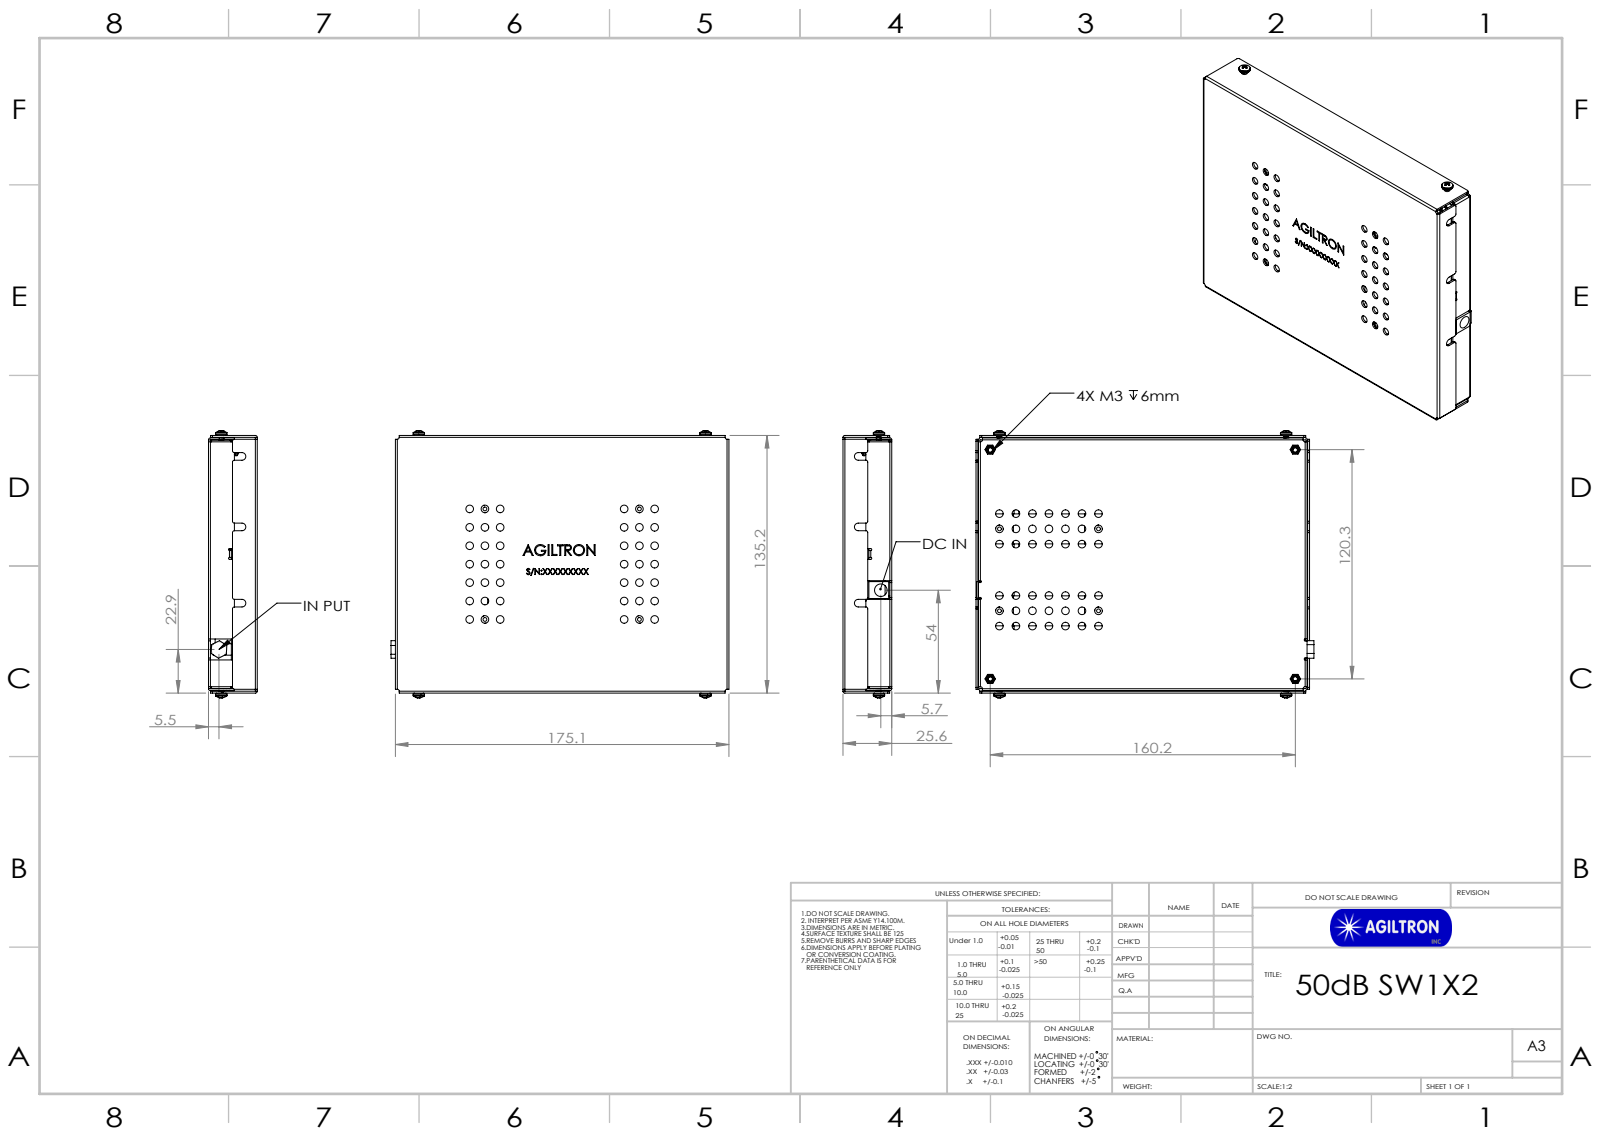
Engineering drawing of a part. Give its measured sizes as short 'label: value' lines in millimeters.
name: BOTTOM COVER BRIDGE; 1001867_3 EO BOTTOM COVER ASM; 1001868_3EO COVER TOP ASM; 92000A116_Passivated 18-8 Stainless Steel Pan Head Phillips Screws (1)_92000A116 (+8 more)
written by: SolidWorks 2017 (CONFIG_CONTROL_DESIGN)
unit: mm
bodies: 31 solids, 1193 faces (535 planar, 394 cylindrical, 264 other)
size: 177.4 × 140.09 × 25.6
volume: 135 252 mm³; area: 197 420 mm²
holes: 84× ⌀4, 14× ⌀4.2, 8× ⌀2, 6× ⌀2.55, 4× ⌀3.5, 1× ⌀6.6
bosses: 8× ⌀6.3, 6× ⌀4.19, 6× ⌀3.59, 6× ⌀3, 1× ⌀6
rounds: 96× R0.29, 46× R1, 23× R2, 10× R0.5, 8× R0.2, 8× R1.2
face distances: 1, 24.6, 11, 12, 12.6, 13.6, 23.6, 25.6, 1.6, 1.3
hole spacings: 11.8, 19.1, 8.67, 8, 17.34, 27.21, 18.2, 26.01
